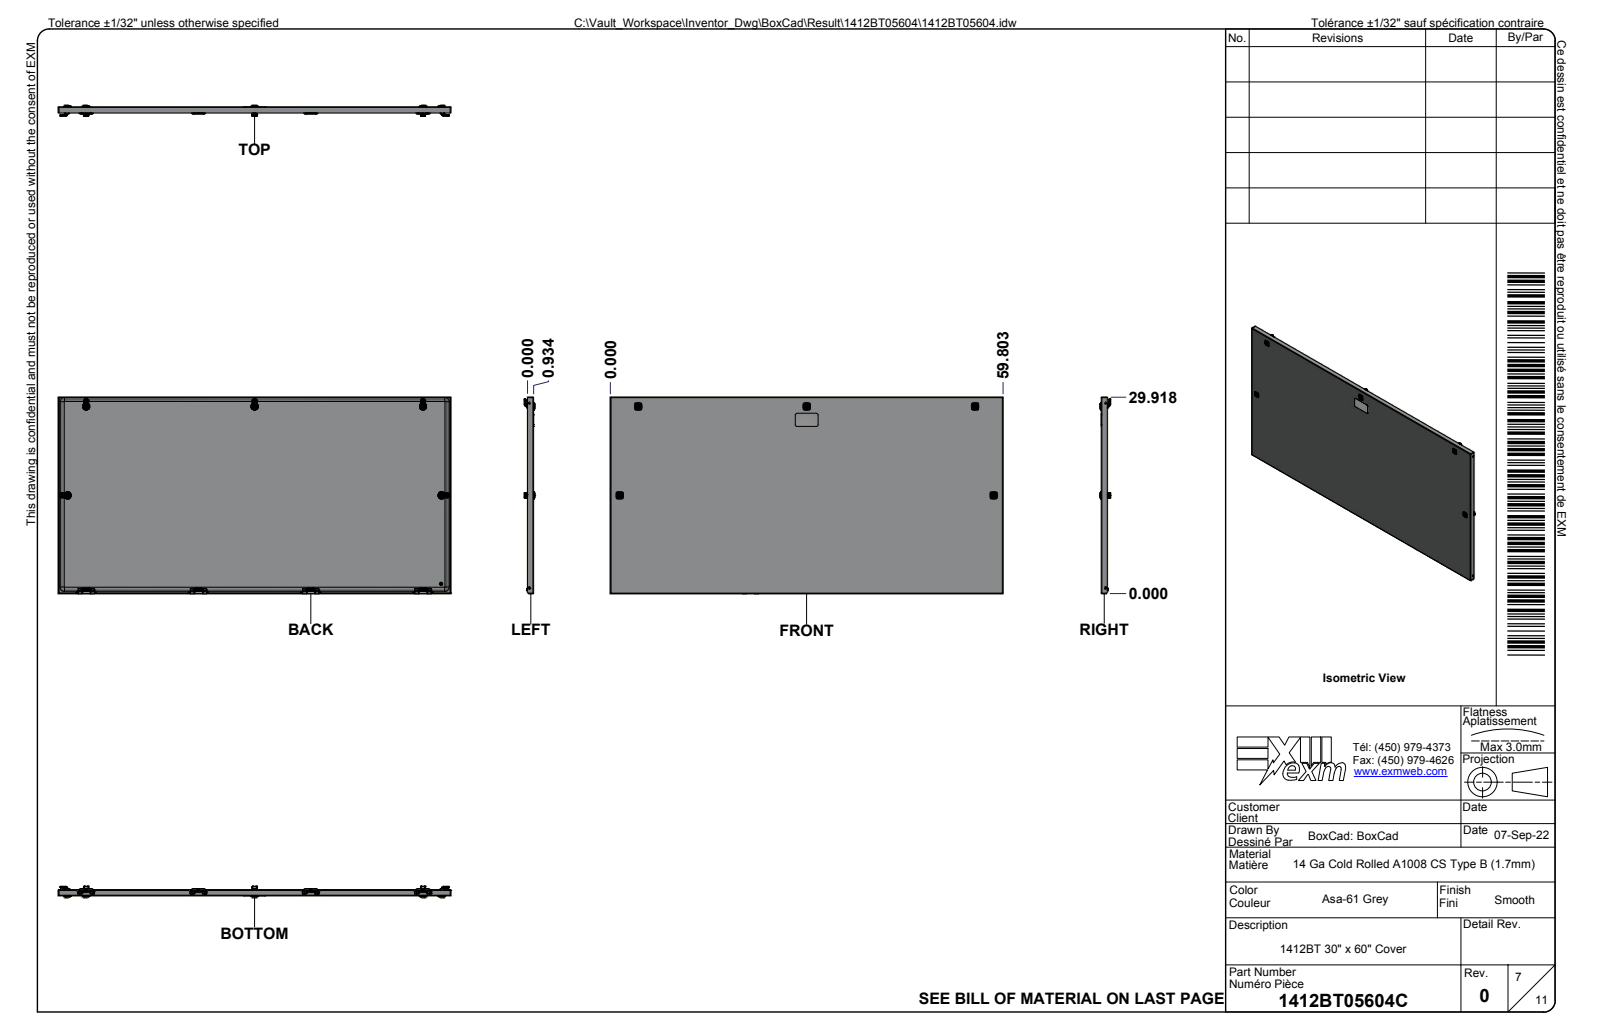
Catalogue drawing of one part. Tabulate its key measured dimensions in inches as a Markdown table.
| quantity | value |
| --- | --- |
| part name | 1412BT05604; 1412BT05604B; 1412BT05604B-P; STK-Q-16005 (+8 more) |
| STEP written by | Autodesk Inventor 2024 (AUTOMOTIVE_DESIGN) |
| units | inches |
| bodies | 216 solids, 32882 faces (12641 planar, 7960 cylindrical, 12281 other) |
| overall size | 60 × 32.25 × 11.588 |
| volume | 707.6 in³ |
| surface area | 15 905 in² |
| round holes (diameter × count) | 0.177 × 48, 0.453 × 24, 0.27 × 18, 0.043 × 16, 0.262 × 12, 0.562 × 12, 0.571 × 12, 0.03 × 10, 0.315 × 10, 0.201 × 9, 0.178 × 8, 0.311 × 5 |
| round bosses / shafts (diameter × count) | 0.472 × 16, 0.039 × 16, 0.307 × 12, 0.232 × 11, 0.03 × 10, 0.311 × 8, 0.262 × 8, 0.717 × 6 |
| partial cylindrical surfaces (radius × count) | 0.02 × 565, 0.031 × 368, 0.039 × 323, 0.01 × 305, 0.008 × 218, 0.012 × 164, 0.004 × 110, 0.016 × 110 |
| main face-to-face distances | 0.068, 11.052, 10.983, 11.12, 29.932, 0.068, 1.01, 0.942, 10.042, 10.11 |
| hole center spacings | 16.5, 0.61, 17.11, 17.657, 15.89, 33.593, 17.101, 34.202 |
